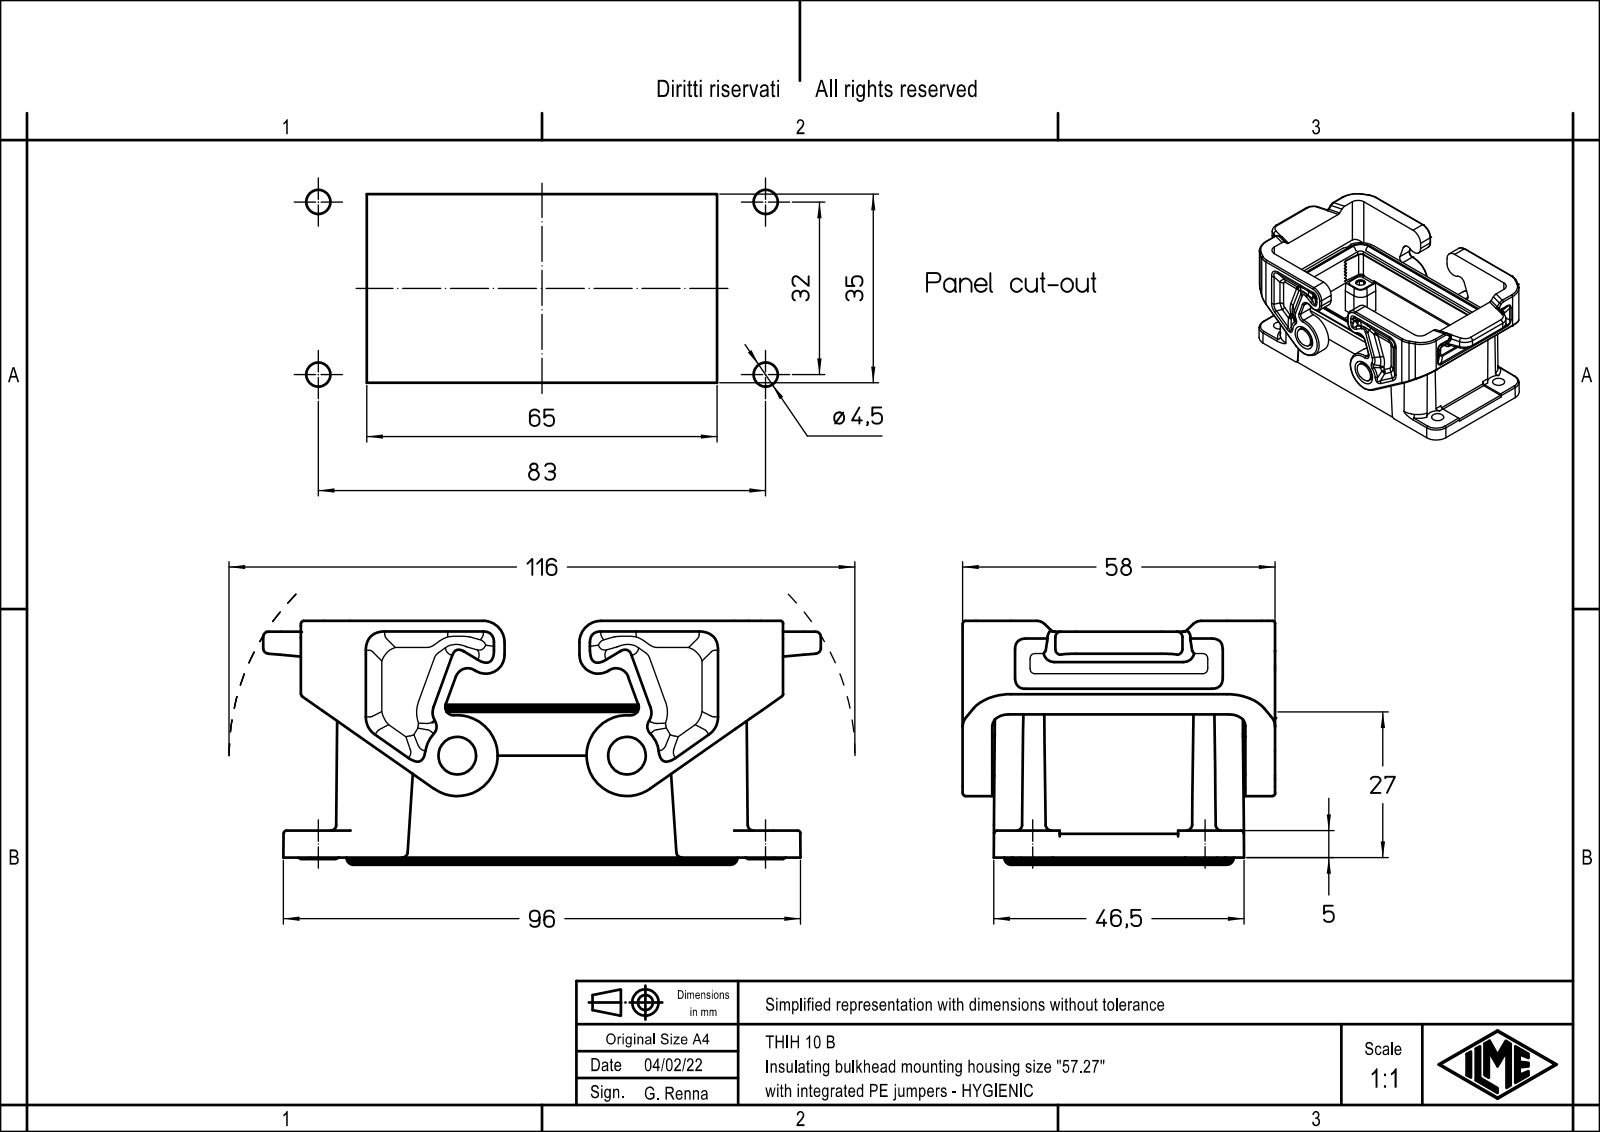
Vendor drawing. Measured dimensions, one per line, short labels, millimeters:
name: 53621; THIH_10
written by: Creo Elements/Direct Modeling 20.1B 02-Apr-2019 (C) Parametric Technology GmbH (AUTOMOTIVE_DESIGN)
unit: mm
bodies: 1 solid, 869 faces (452 planar, 249 cylindrical, 168 other)
size: 103.5 × 58 × 45.25
volume: 64 811 mm³; area: 37 337 mm²
holes: 4× ⌀2.5, 4× ⌀3.5, 4× ⌀4.5, 2× ⌀7.2
bosses: 4× ⌀4.8, 2× ⌀7
rounds: 25× R1, 20× R1.3, 18× R1.5, 16× R2, 12× R3, 12× R5.5, 8× R5, 8× R6
face distances: 40.6, 5.5, 52.5, 47, 40.4, 70.61, 45.9, 12.1, 6.3, 46.2
hole spacings: 13.24, 32.24, 70.04, 75.96, 27, 32, 57, 63.07
